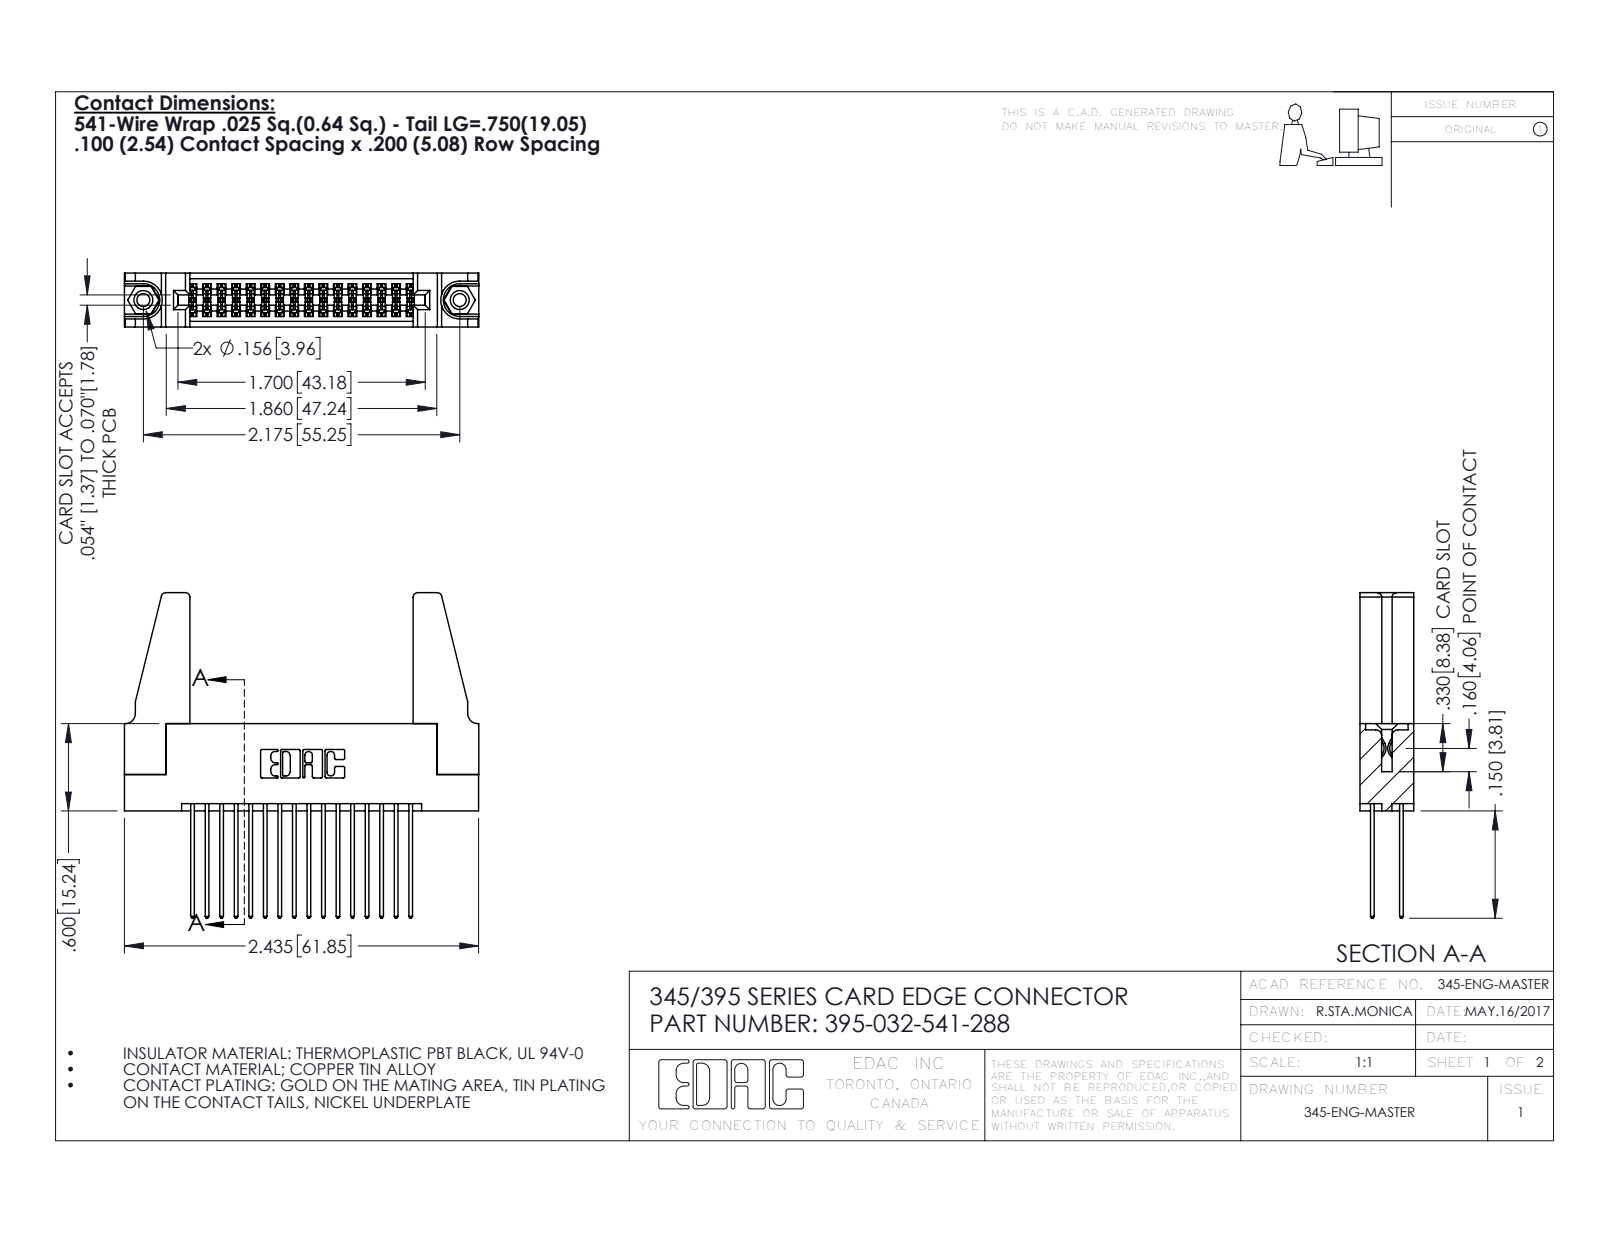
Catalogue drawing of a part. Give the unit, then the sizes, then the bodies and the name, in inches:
Units: inches
Overall size (bounding box): 2.436 × 2.237 × 0.37
Round holes (diameter × count): ⌀0.089 ×2, ⌀0.125 ×2, ⌀0.156 ×2, ⌀0.064 ×1
Round bosses / shafts (diameter × count): ⌀0.155 ×2
Partial cylindrical surfaces — rounded edges, fillets, slot ends (radius × count): R0.006 ×48, R0.01 ×32, R0.01 ×22, R0.03 ×8, R0.007 ×6, R0.031 ×6, R0.026 ×3, R0.014 ×2
Main face-to-face distances: 0.072, 0.298, 0.2, 0.37, 0.098, 0.272, 0.025, 0.225, 0.175, 0.148
Hole centre spacings: 0.27, 1.942, 2.175
Volume: 0.562 in³ · Surface area: 19.04 in²
Bodies: 37 solids, 1850 faces (1208 planar, 626 cylindrical, 16 other)
Part name (STEP PRODUCT): 345-220-078_345-220-088; 345 Part_Flush Mounting Lugs - 0.156 Dia-TH; 345-250-001_345-250-001-102; 345-292-001_345-293-141 (+1 more)
STEP written by: SolidWorks 2016 (CONFIG_CONTROL_DESIGN)
